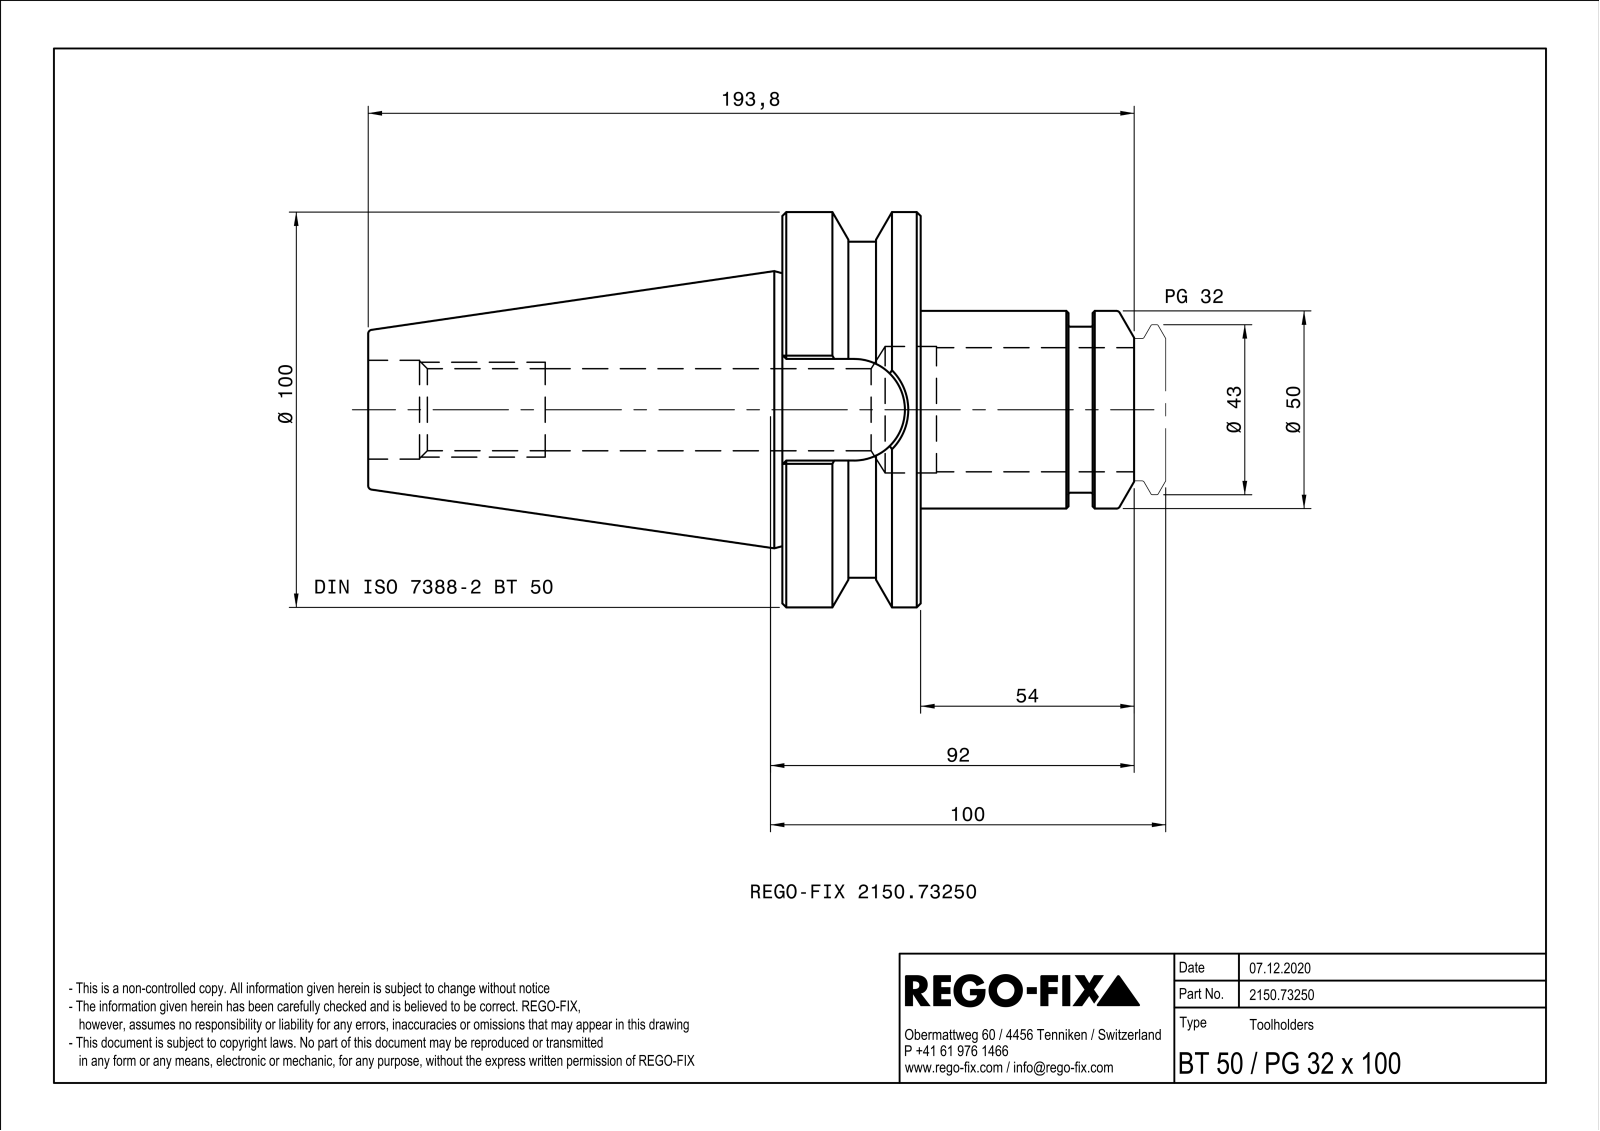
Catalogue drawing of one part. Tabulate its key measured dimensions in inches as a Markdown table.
| quantity | value |
| --- | --- |
| part name | NOCUT |
| STEP written by | SIEMENS PLM Software Solid Edge ST10 (AUTOMOTIVE_DESIGN) |
| units | inches |
| bodies | 1 solid, 80 faces (31 planar, 18 cylindrical, 31 other) |
| overall size | 7.63 × 3.937 × 3.937 |
| volume | 30.3 in³ |
| surface area | 104.7 in² |
| round holes (diameter × count) | 0.817 × 1, 0.984 × 1, 1.299 × 1 |
| round bosses / shafts (diameter × count) | 3.937 × 1, 3.346 × 1, 1.969 × 1, 1.654 × 1 |
| partial cylindrical surfaces (radius × count) | 0.02 × 4, 0.506 × 1 |
| main face-to-face distances | 1.378, 2.783, 5.504, 4.126, 1.472, 2.85, 6.976, 0.24, 1.713, 3.091 |
